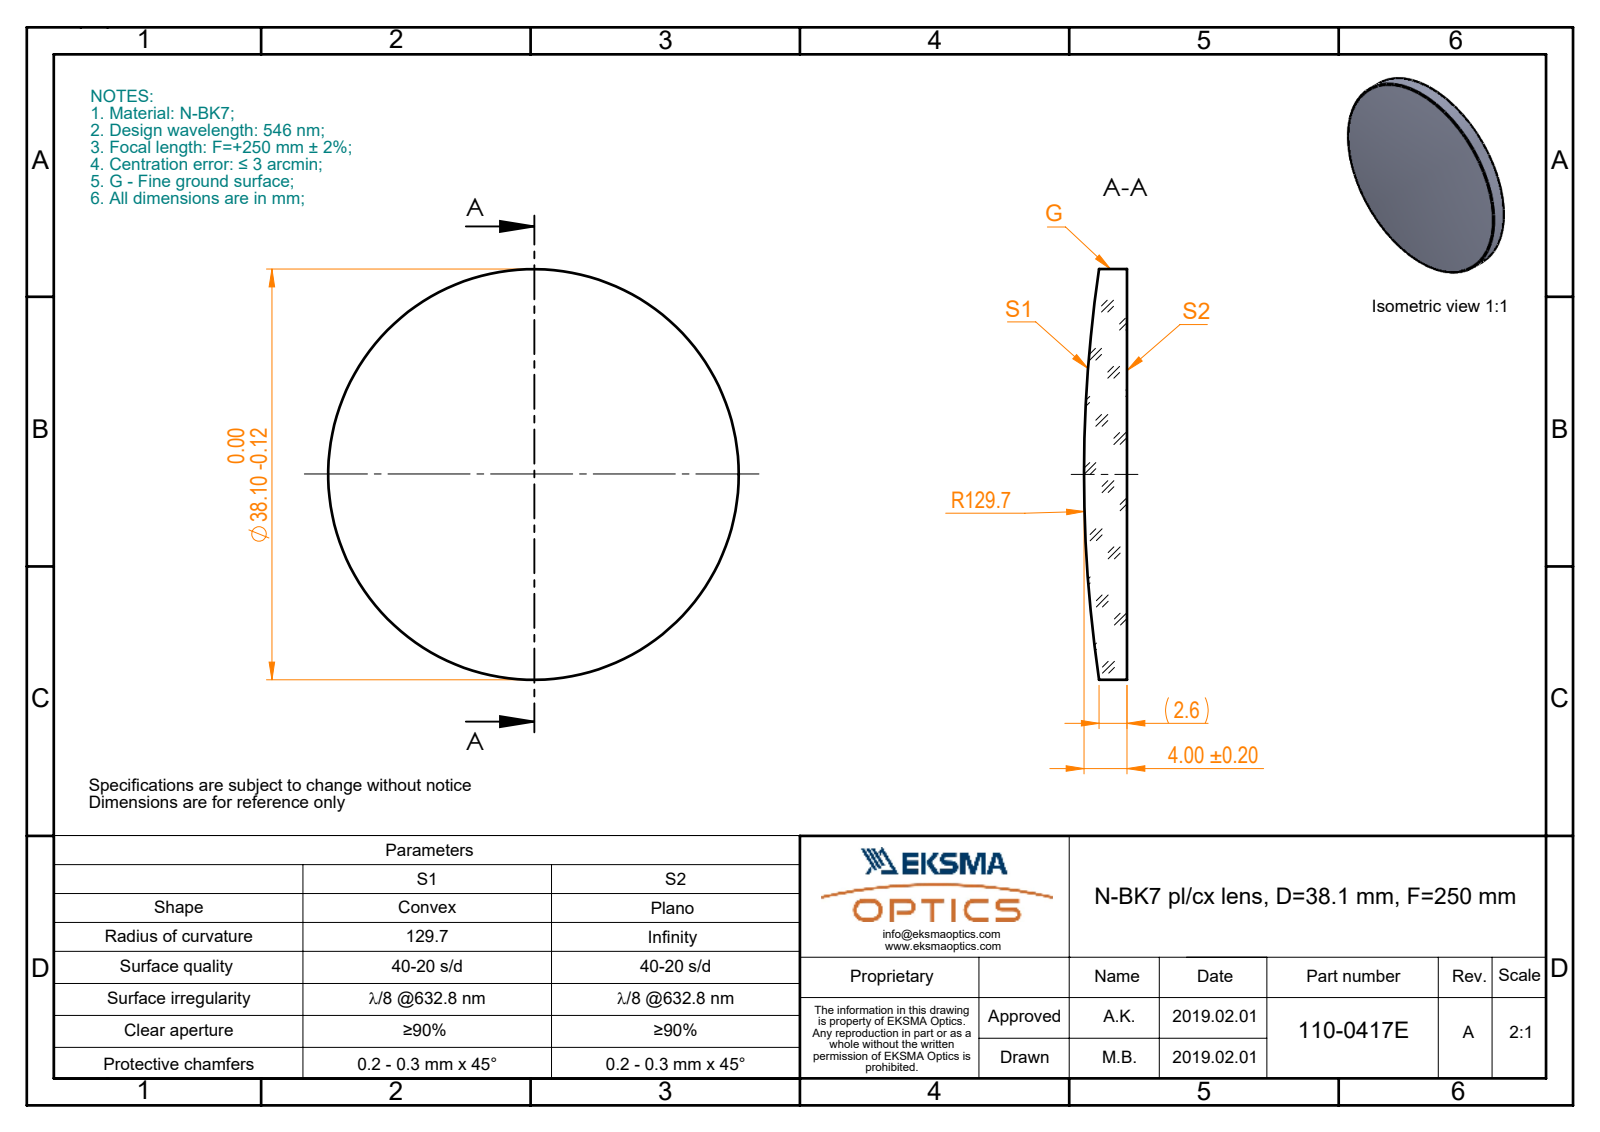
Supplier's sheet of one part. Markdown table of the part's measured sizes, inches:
| quantity | value |
| --- | --- |
| part name | 110-0417E BK7 pl-cx 38.1 F250 |
| STEP written by | SolidWorks 2017 (CONFIG_CONTROL_DESIGN) |
| units | inches |
| bodies | 1 solid, 5 faces (1 planar, 2 cylindrical, 2 other) |
| overall size | 1.5 × 1.5 × 0.157 |
| volume | 0.229 in³ |
| surface area | 4.025 in² |
| round bosses / shafts (diameter × count) | 1.5 × 1 |
